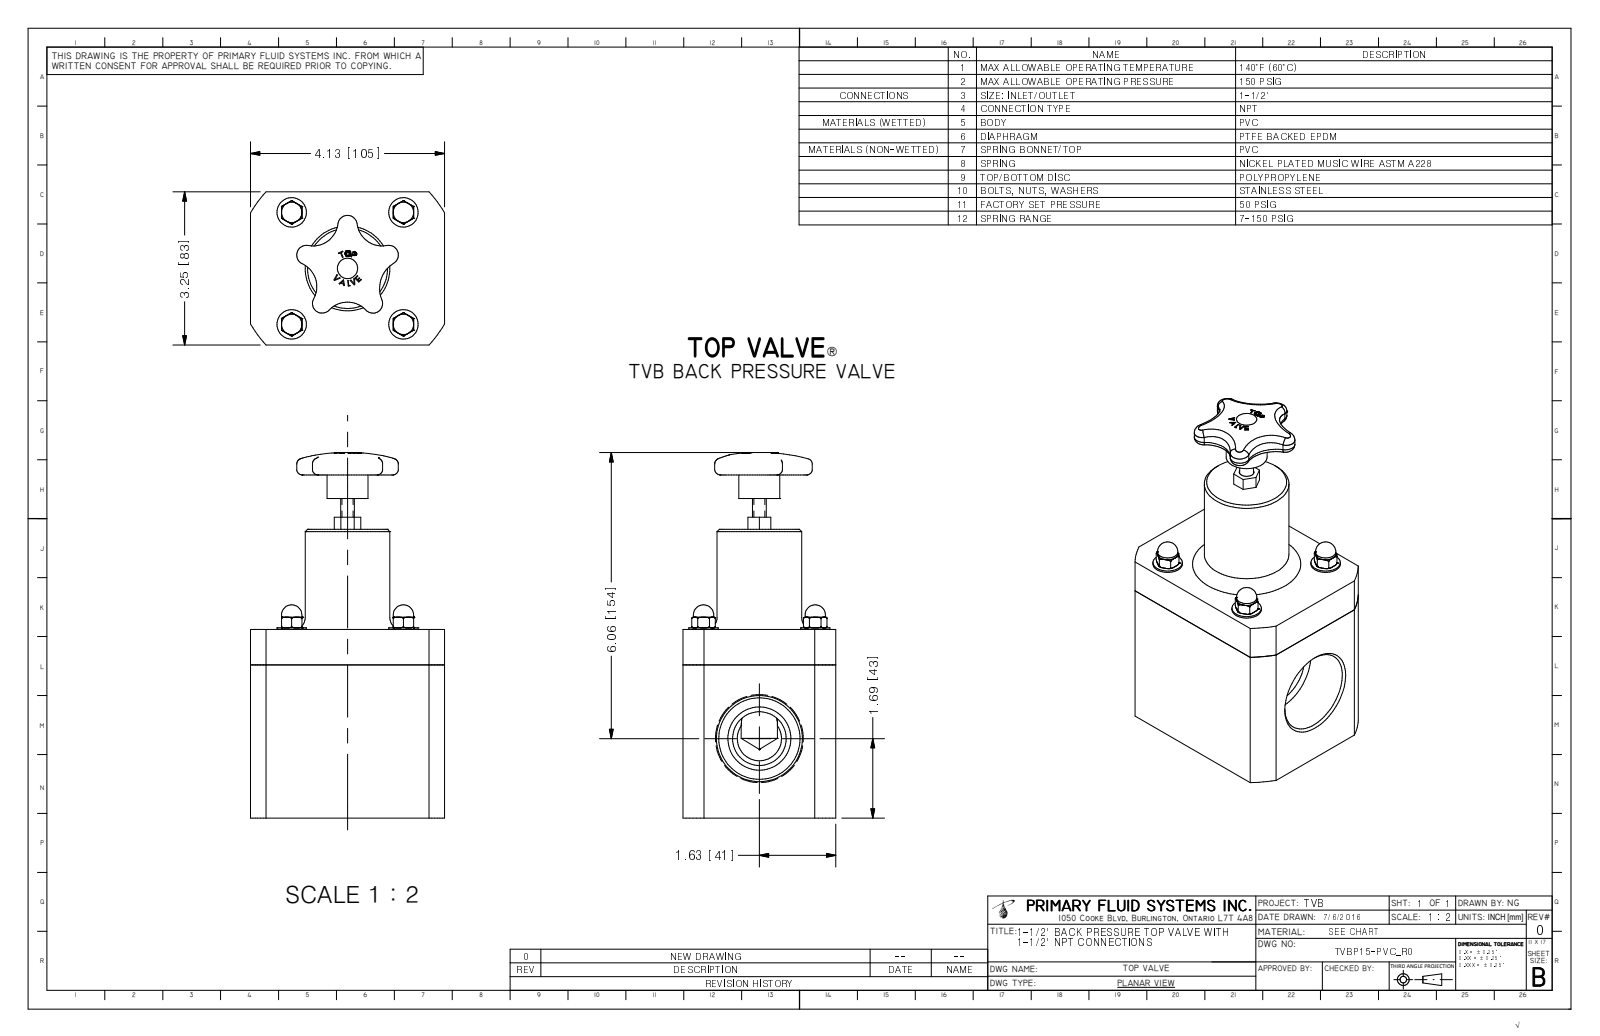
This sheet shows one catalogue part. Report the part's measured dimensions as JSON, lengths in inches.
{"part_name": "TVBP15-PVC_R0", "step_written_by": "Autodesk Inventor 2009 (AUTOMOTIVE_DESIGN)", "units": "inches", "bodies": {"solids": 1, "faces": 337, "planar": 144, "cylindrical": 45, "other": 148}, "overall_size": [7.752, 4.125, 3.25], "volume_in3": 54.78, "surface_area_in2": 119.8, "round_holes": [[0.175, 4], [1.727, 1]], "round_bosses_or_shafts": [[0.625, 4], [0.433, 4], [0.375, 4], [1.8, 1], [0.87, 1], [0.293, 1]], "partial_cylinders_radius": [[0.085, 5], [0.205, 5], [0.536, 4], [0.656, 4], [0.625, 1], [0.745, 1], [2.375, 1]], "face_to_face_distances": [3.25, 4, 4.125, 1, 3.125, 2.125, 6.125, 0.433, 4.036, 0.036], "hole_center_spacings": [2.375, 2.375, 3.359]}
